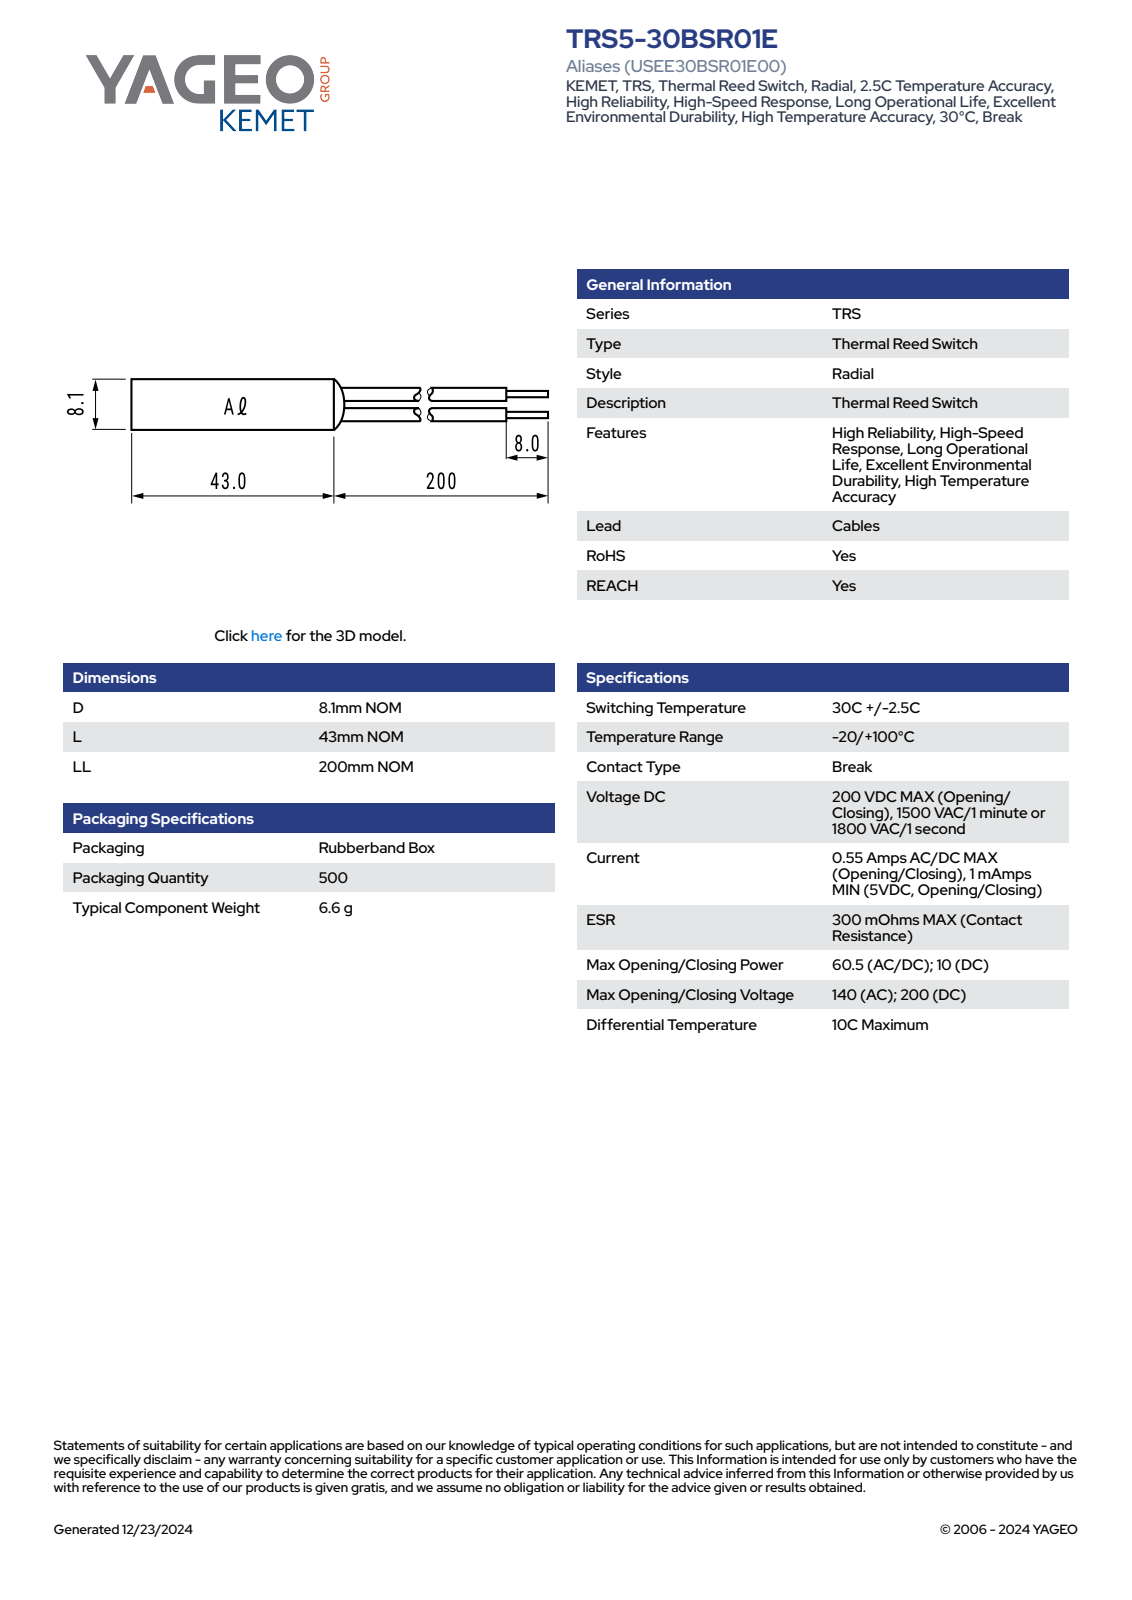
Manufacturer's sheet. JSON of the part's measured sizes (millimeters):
{"part_name": "ST_TSR01E_D8.1L43LL200", "step_written_by": "SolidWorks 2014 (AUTOMOTIVE_DESIGN)", "units": "millimeters", "bodies": {"solids": 1, "faces": 72, "planar": 63, "cylindrical": 8, "other": 1}, "overall_size": [243, 8.11, 8.1], "volume_mm3": 4068, "surface_area_mm2": 3955, "round_bosses_or_shafts": [[2, 2], [0.5, 2]], "face_to_face_distances": [8.1, 235, 8, 243, 2.03, 6.07, 4.04, 2.8, 5.3, 0.77]}
